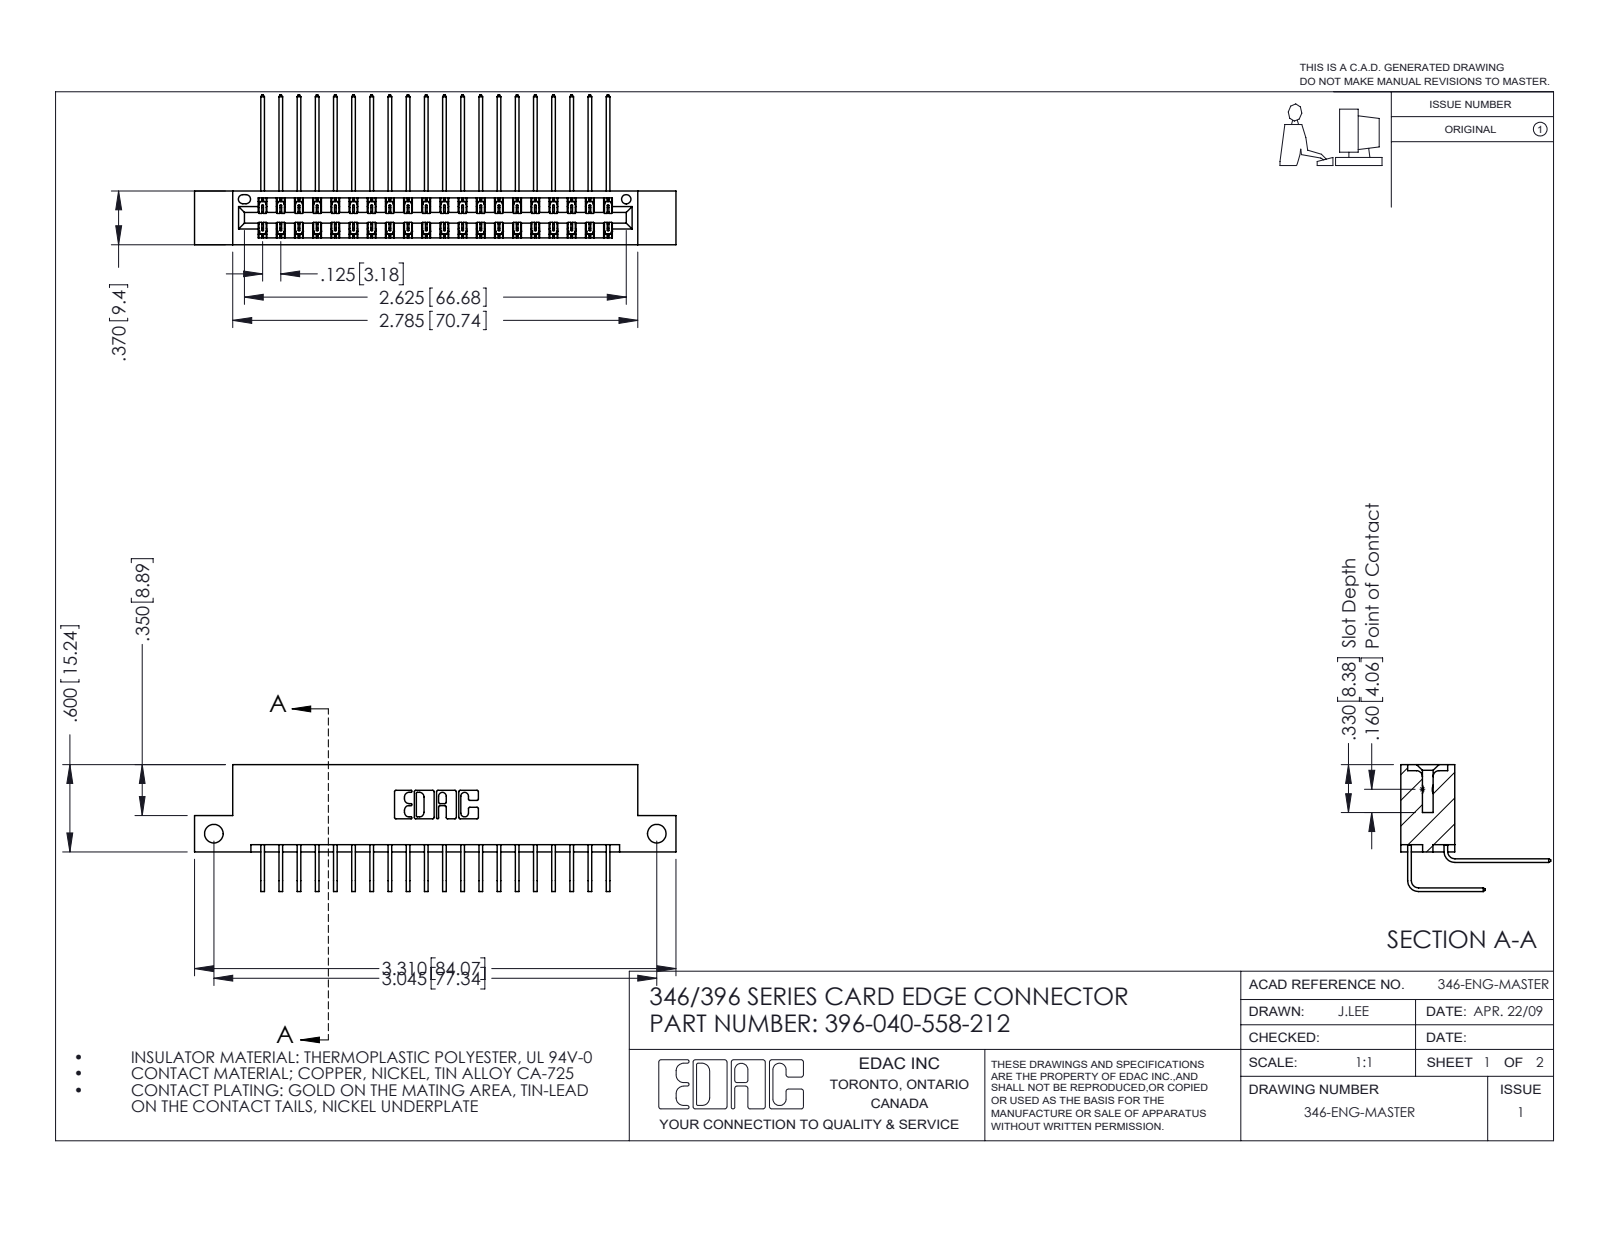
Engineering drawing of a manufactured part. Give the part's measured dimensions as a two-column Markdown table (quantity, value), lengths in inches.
| quantity | value |
| --- | --- |
| part name | 345-292-001_558 559 Tail - 1; 396-040-558-212; 345-292-001_558 Tail - 2; 346 Part_Flush Mounting Lugs - Side Mount |
| STEP written by | SolidWorks 2016 (CONFIG_CONTROL_DESIGN) |
| units | inches |
| bodies | 41 solids, 2282 faces (1556 planar, 726 cylindrical, 0 other) |
| overall size | 3.31 × 1.03 × 0.873 |
| volume | 0.499 in³ |
| surface area | 18.38 in² |
| round holes (diameter × count) | 0.128 × 2, 0.064 × 1 |
| partial cylindrical surfaces (radius × count) | 0.006 × 60, 0.01 × 22, 0.007 × 6, 0.031 × 6, 0.026 × 3, 0.014 × 2, 0.022 × 2, 0.024 × 2 |
| main face-to-face distances | 0.322, 0.048, 0.25, 0.025, 0.37, 0.298, 0.072, 0.275, 0.148, 0.222 |
| hole center spacings | 3.045 |
